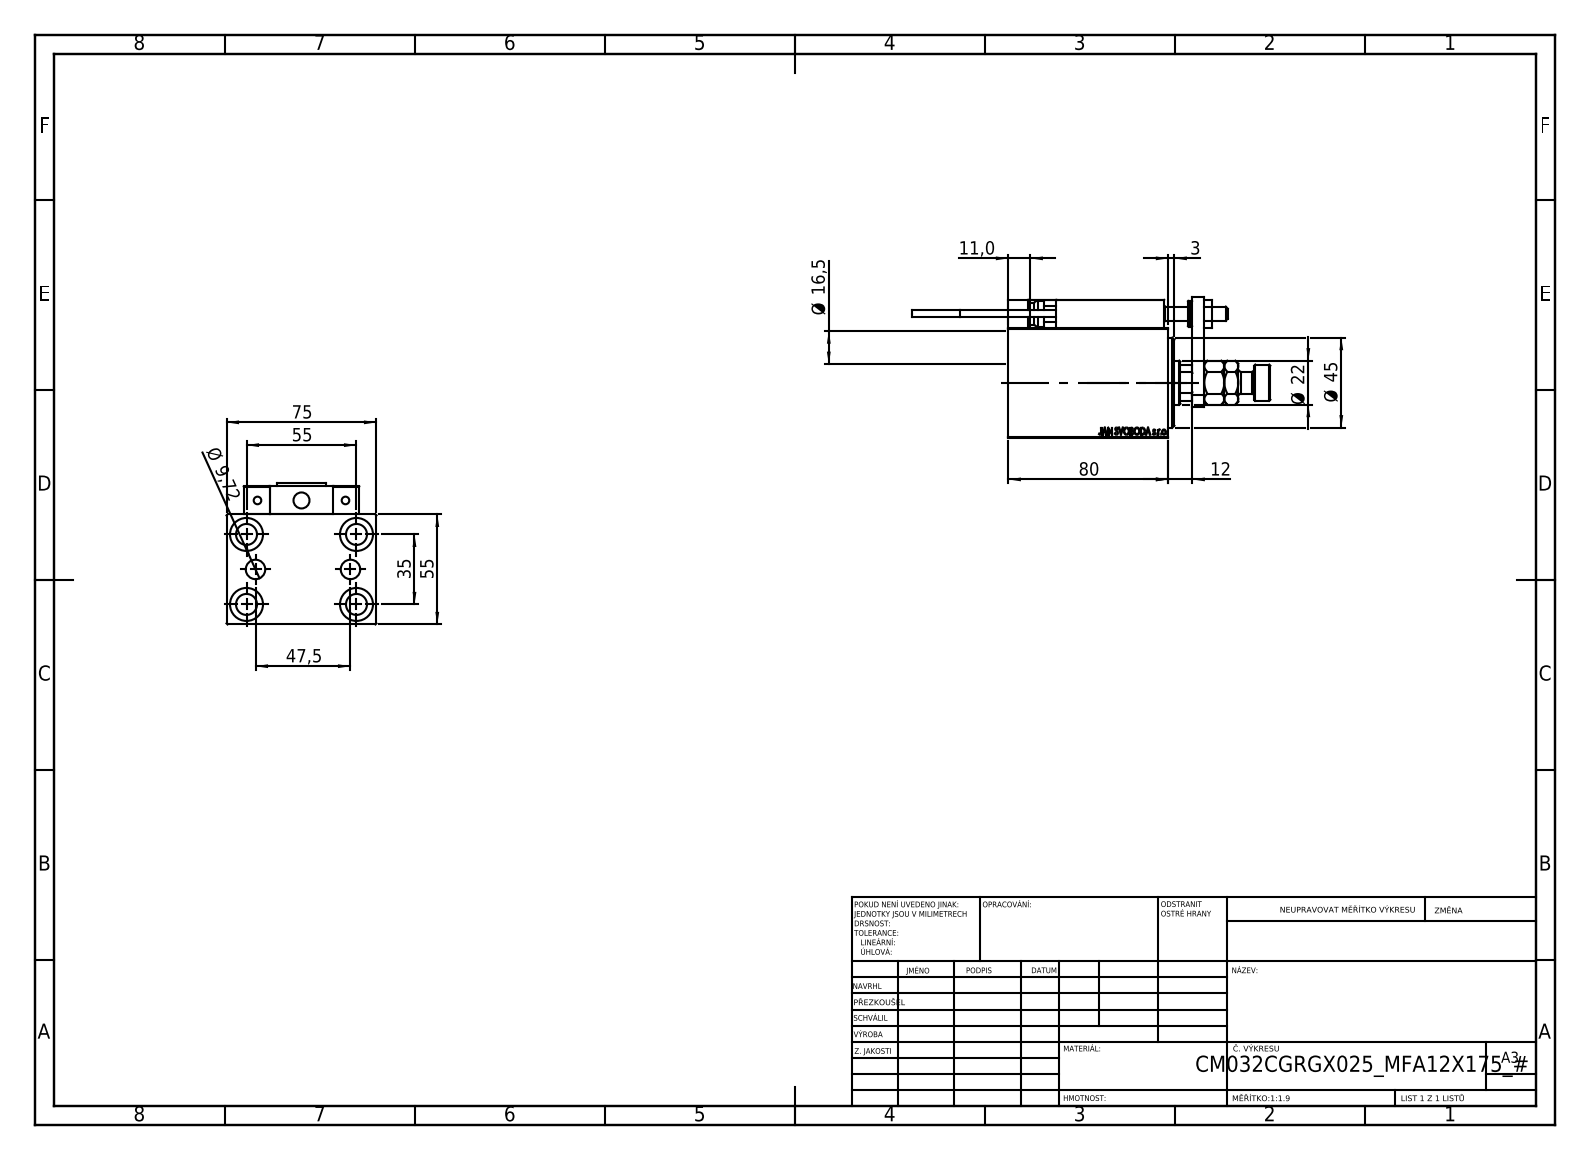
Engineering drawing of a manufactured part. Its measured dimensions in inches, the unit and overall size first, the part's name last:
Units: inches
Overall size (bounding box): 7.047 × 2.953 × 2.776
Round holes (diameter × count): ⌀0.315 ×5, ⌀0.413 ×5, ⌀0.65 ×5, ⌀0.126 ×4, ⌀0.157 ×4, ⌀0.197 ×2, ⌀0.383 ×2, ⌀0.276 ×1, ⌀0.866 ×1, ⌀1.004 ×1, ⌀1.26 ×1, ⌀1.339 ×1
Round bosses / shafts (diameter × count): ⌀0.433 ×2, ⌀0.197 ×2, ⌀0.15 ×2, ⌀0.709 ×1, ⌀0.512 ×1
Partial cylindrical surfaces — rounded edges, fillets, slot ends (radius × count): R0.012 ×30, R0.118 ×2, R0.413 ×1
Main face-to-face distances: 2.165, 2.953, 0.551, 2.717, 0.394, 0.472, 2.283, 0.984, 0.276, 0.118
Hole centre spacings: 1.283, 0.448, 0.699, 0.711, 0.787, 1.165, 1.169, 1.262
Volume: 20.78 in³ · Surface area: 138.7 in²
Bodies: 24 solids, 1324 faces (574 planar, 184 cylindrical, 566 other)
Part name (STEP PRODUCT): MAGNET; V450CM_C_VCP; SWITCH X; Block (+8 more)
STEP written by: SolidWorks 2019 (CONFIG_CONTROL_DESIGN)
